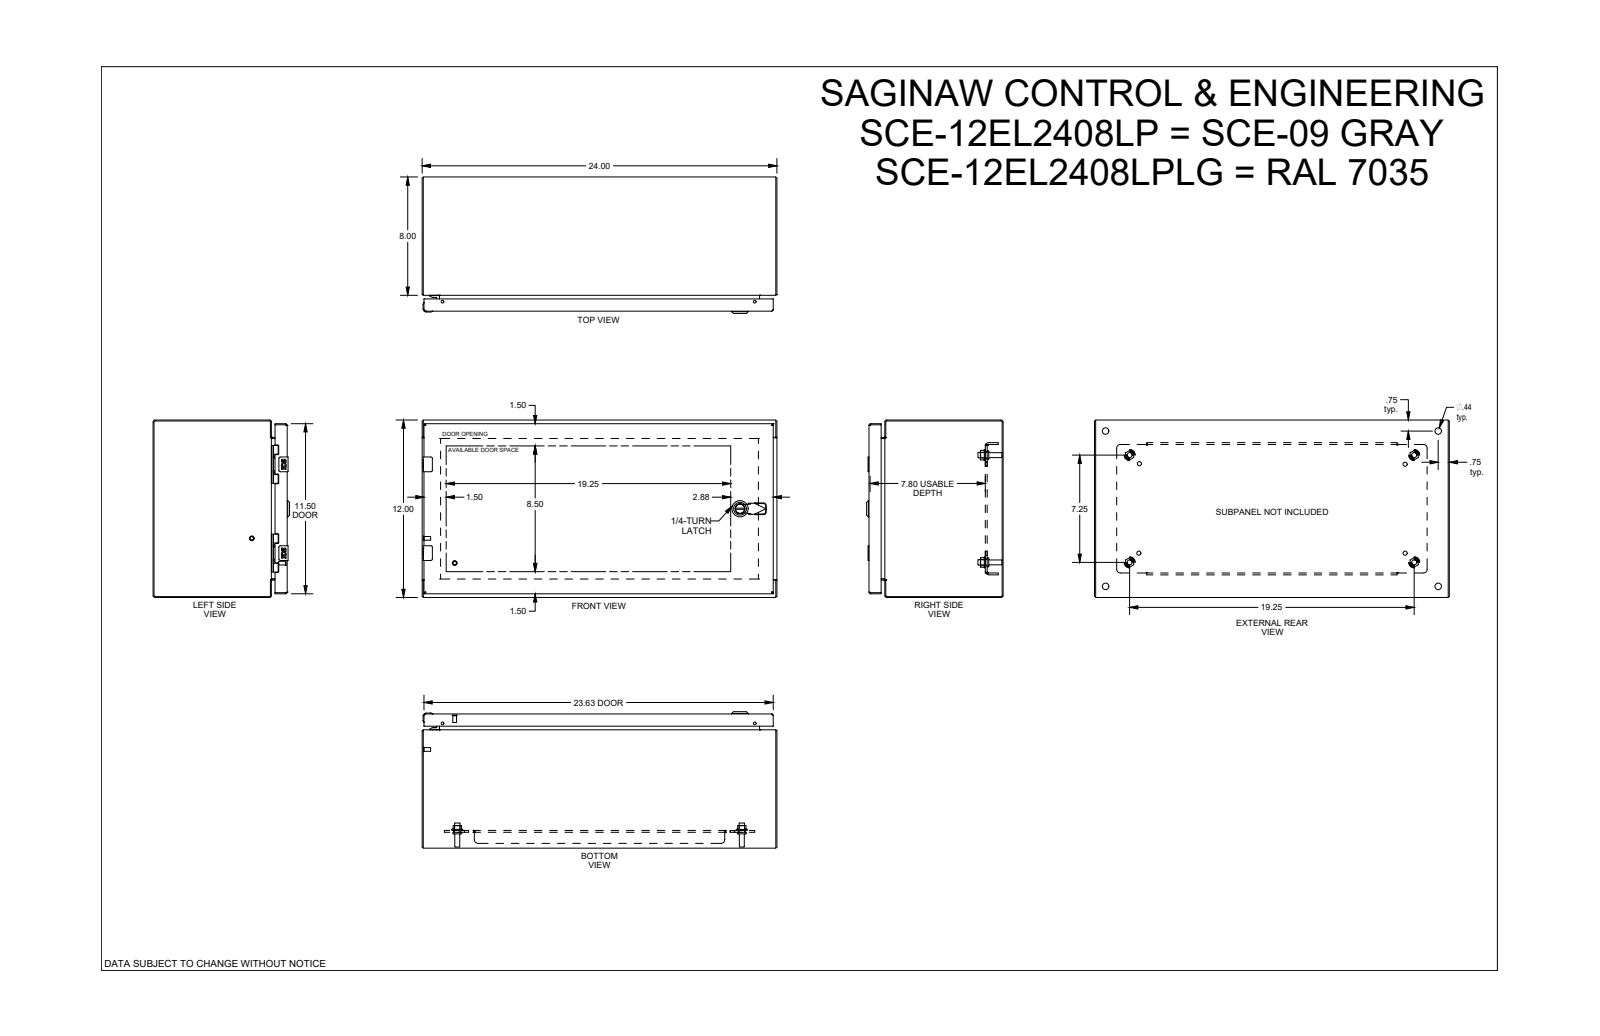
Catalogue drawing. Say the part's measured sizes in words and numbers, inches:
The part is named "SCE-12EL2408LP". Its 3-D file was written by "SolidWorks 2019 (AUTOMOTIVE_DESIGN)". It is 37 solids with 1695 faces: 846 planar, 511 cylindrical and 338 other. Overall it measures 24 by 12 by 9.23 inches. Its volume is 132.4 cubic inches and its surface area 3 222 square inches. Round holes: 4 of diameter 0.172, 4 of diameter 0.205, 4 of diameter 0.244, 4 of diameter 0.266, 4 of diameter 0.281, 4 of diameter 0.367, 4 of diameter 0.375, 4 of diameter 0.437, 4 of diameter 0.5, 2 of diameter 0.04, 2 of diameter 0.188, 2 of diameter 0.218. Round bosses or shafts: 6 of diameter 0.17, 4 of diameter 0.366, 4 of diameter 0.332, 4 of diameter 0.25, 4 of diameter 0.24, 3 of diameter 0.196, 2 of diameter 0.248, 1 of diameter 1.102. Partial cylindrical surfaces (rounded edges, fillets, slot ends): 30 of radius 0.012, 28 of radius 0.01, 24 of radius 0.015, 13 of radius 0.06, 12 of radius 0.02, 12 of radius 0.1, 10 of radius 0.031, 10 of radius 0.117. The main face-to-face distances are 0.075, 11.925, 0.06, 8.938, 9.073, 8.998, 9.013, 1, 0.125, 23.925. The hole center spacings are 0.985, 6, 0.02, 0.493, 0.494, 0.875, 2.743, 6.66.
